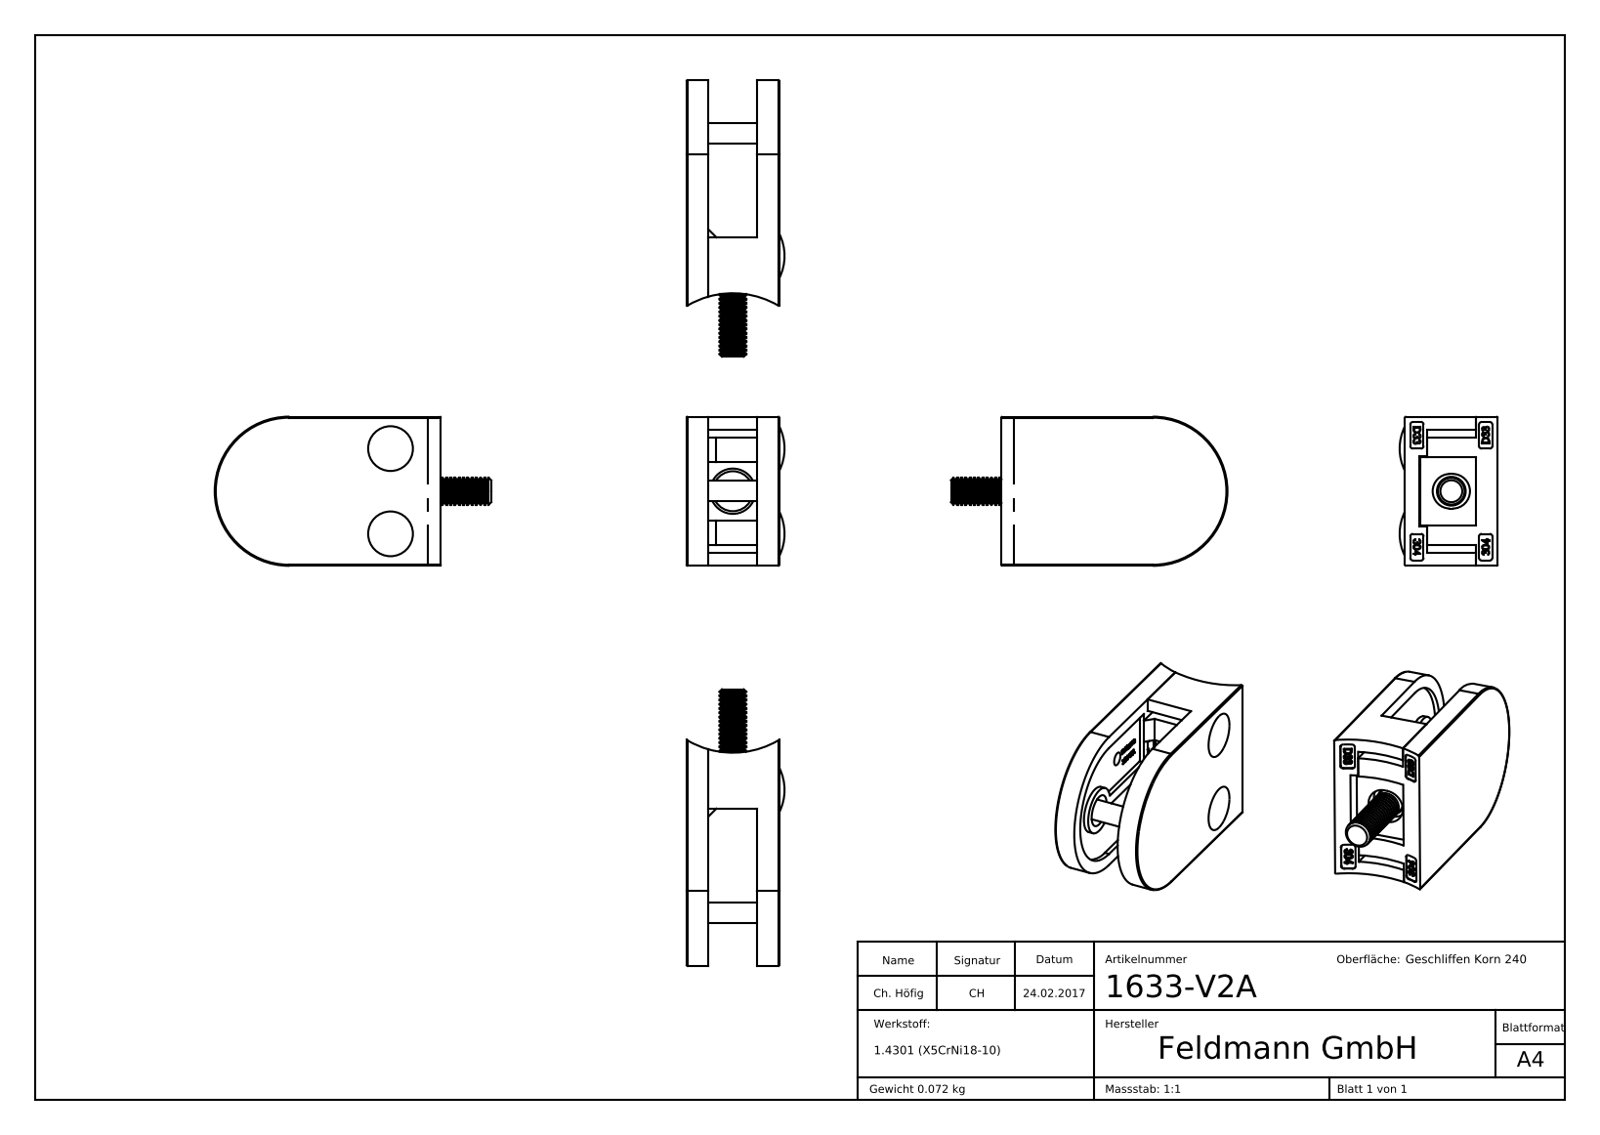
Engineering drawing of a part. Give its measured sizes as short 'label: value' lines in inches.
name: socket countersunk head screw_din_DIN 7991 - M4 x 10 --- 10S; socket head thin cap screw_din_DIN 7984 - M5 x 16 --- 16S; 16-Kappe_16-Kappe; 16xx-XXX Teil1_1633-V2A (+3 more)
written by: SolidWorks 2015 (CONFIG_CONTROL_DESIGN)
unit: in
bodies: 8 solids, 1429 faces (616 planar, 204 cylindrical, 609 other)
size: 2.043 × 1.102 × 0.724
volume: 0.601 in³; area: 14.06 in²
holes: 2× ⌀0.039, 2× ⌀0.098, 2× ⌀0.13, 2× ⌀0.163, 2× ⌀0.323, 1× ⌀0.154, 1× ⌀0.236
bosses: 2× ⌀0.301, 2× ⌀0.157, 2× ⌀0.098, 1× ⌀0.346, 1× ⌀0.335, 1× ⌀0.197, 1× ⌀0.152
rounds: 20× R0.02, 4× R0.008, 2× R0.128, 1× R0.457, 1× R0.551, 1× R0.663, 1× R0.667
face distances: 0.685, 0.161, 0.524, 0.126, 0.559, 0.035, 0.398, 0.433, 0.362, 0.098
hole spacings: 0.433, 0.555, 0.788, 0.959, 0.496, 0.63
